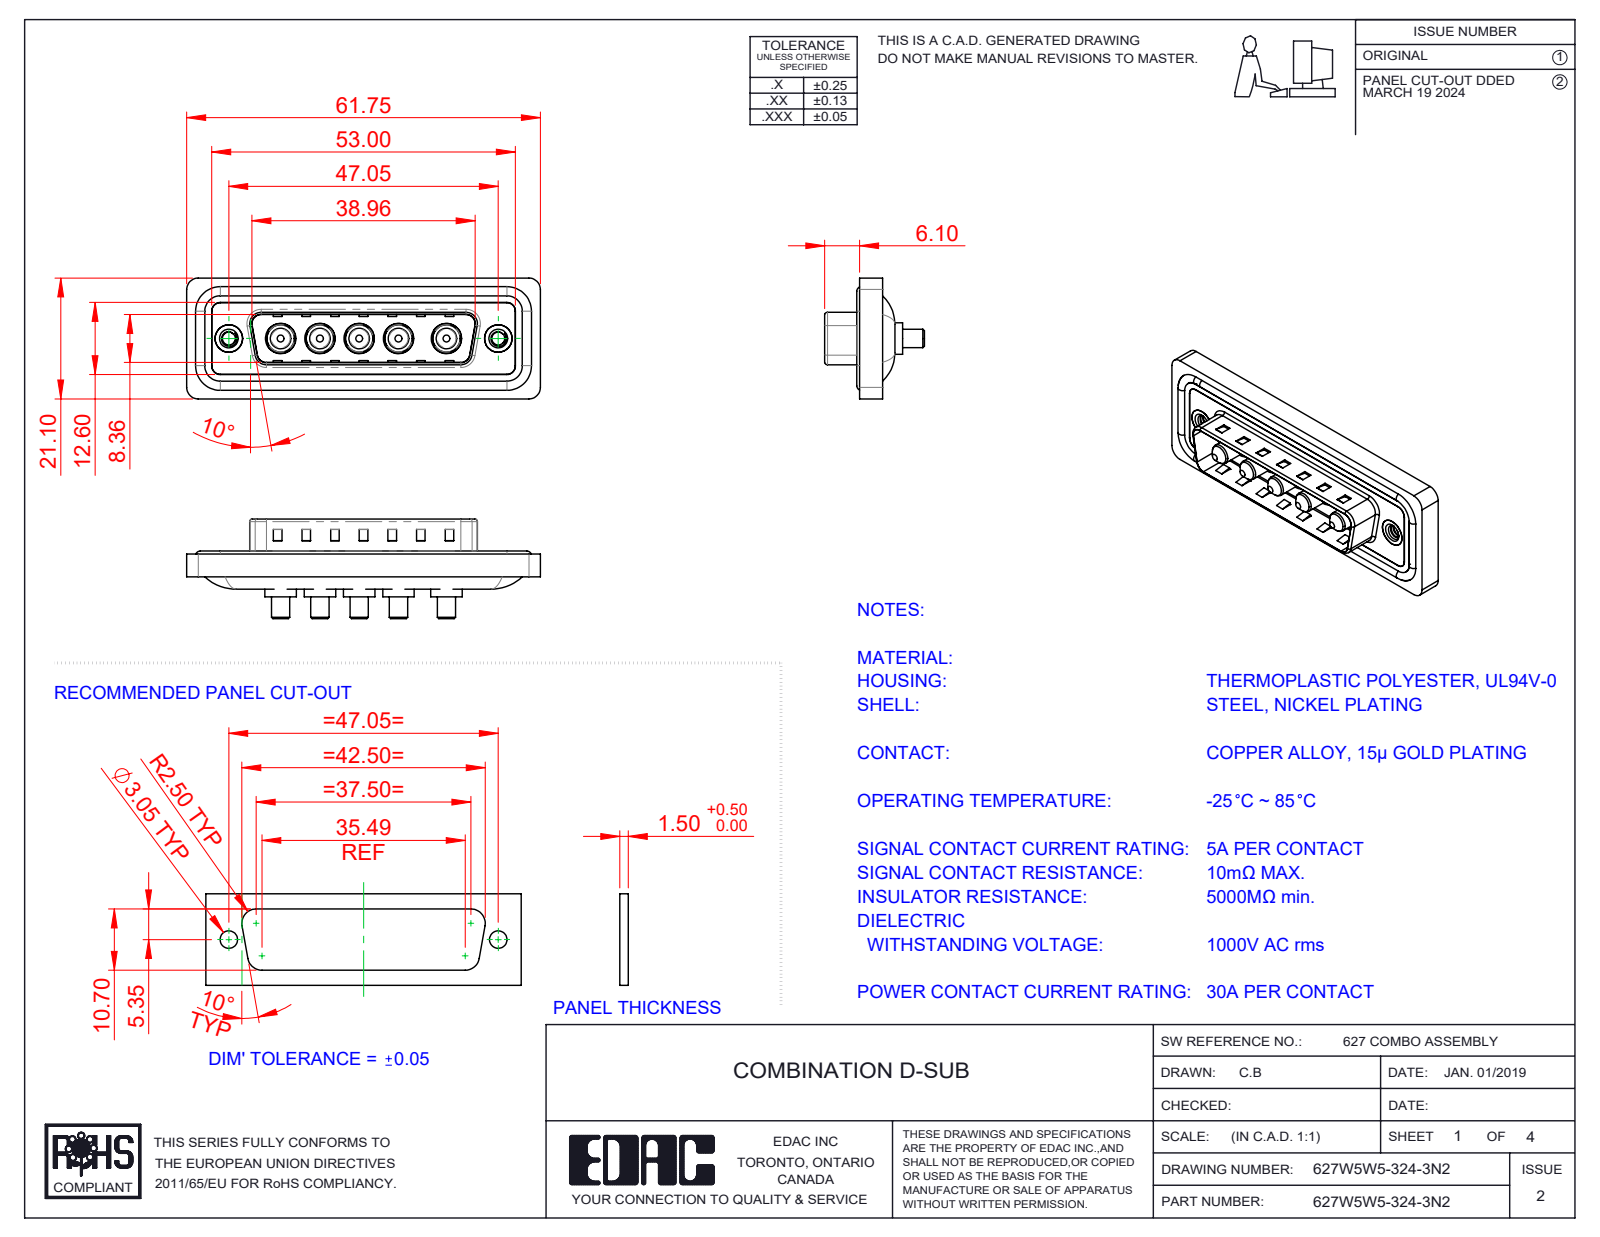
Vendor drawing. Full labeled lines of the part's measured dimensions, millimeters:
Part name (STEP PRODUCT): 627Combo Housing_5W5; Power Pin_30A S; 627Combo Waterproof Housing_25 Contacts; 627Combo Threaded Rivet_2 (+3 more)
STEP written by: SolidWorks 2023 (CONFIG_CONTROL_DESIGN)
Units: millimetres
Bodies: 17 solids, 678 faces (259 planar, 283 cylindrical, 136 other)
Overall size (bounding box): 61.75 × 21.1 × 17.4
Volume: 7 508 mm³ · Surface area: 11 819 mm²
Round holes (diameter × count): ⌀4.85 ×5, ⌀5.3 ×5, ⌀2.26 ×2, ⌀4 ×2, ⌀4.8 ×2, ⌀5 ×2
Round bosses / shafts (diameter × count): ⌀5.5 ×5, ⌀5.2 ×5, ⌀4.75 ×5, ⌀3.75 ×5, ⌀3.6 ×5, ⌀3.2 ×5, ⌀1.6 ×4, ⌀4.9 ×2
Partial cylindrical surfaces — rounded edges, fillets, slot ends (radius × count): R1.5 ×22, R2 ×18, R0.5 ×8, R1.6 ×8, R2.1 ×5, R0.25 ×4, R0.6 ×4, R0.65 ×4
Main face-to-face distances: 0.4, 1.5, 0.5, 1.1, 3.1, 1.6, 2.9, 0.82, 9.58, 5.65
Hole centre spacings: 6.86, 9.04, 13.73, 38.01, 6.87, 8.37, 8.38, 9.05
